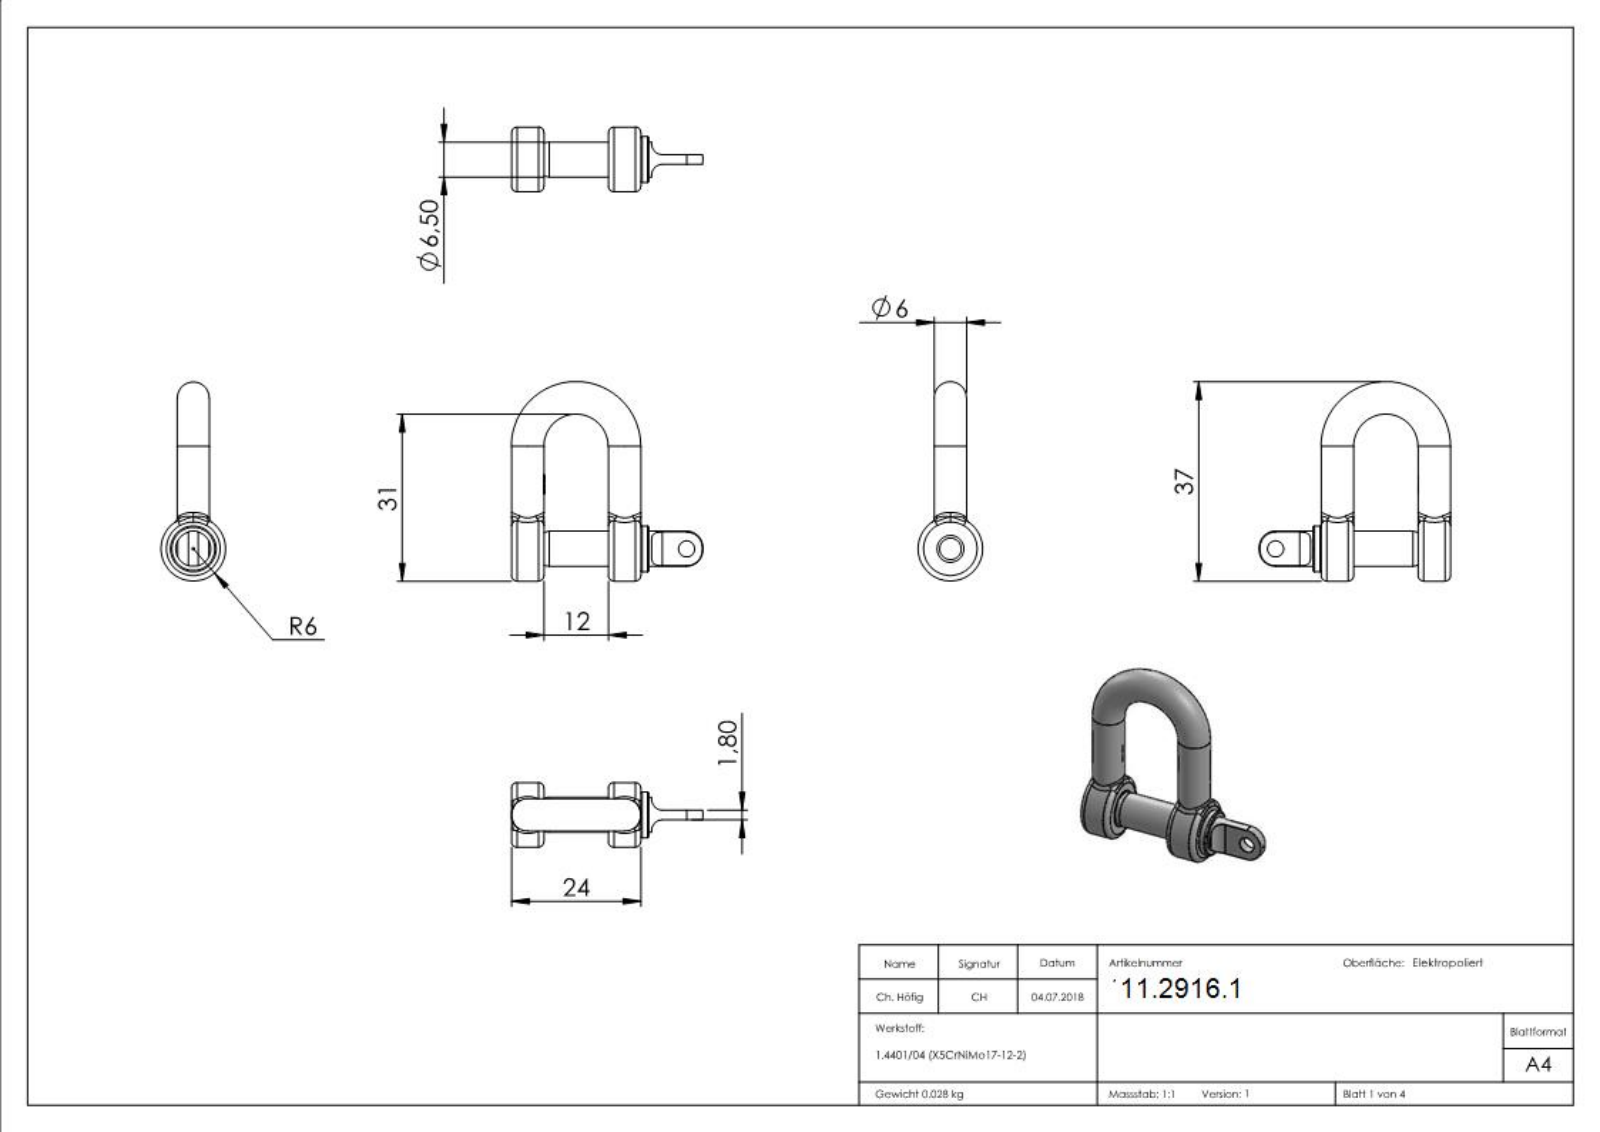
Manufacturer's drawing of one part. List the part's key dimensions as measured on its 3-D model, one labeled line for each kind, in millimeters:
Part name (STEP PRODUCT): 1000500X Teil1_10005006 Teil1; 10005006; 1000500X Teil2_10005006 Teil2
STEP written by: SolidWorks 2015 (CONFIG_CONTROL_DESIGN)
Units: millimetres
Bodies: 2 solids, 305 faces (74 planar, 64 cylindrical, 167 other)
Overall size (bounding box): 37 × 35.51 × 12
Volume: 3 508 mm³ · Surface area: 2 679 mm²
Round holes (diameter × count): ⌀3 ×1, ⌀5 ×1
Round bosses / shafts (diameter × count): ⌀6 ×3, ⌀12 ×1, ⌀8.5 ×1, ⌀6.5 ×1
Partial cylindrical surfaces — rounded edges, fillets, slot ends (radius × count): R2 ×2, R2.98 ×1
Main face-to-face distances: 6, 18, 24, 12, 1.8, 25.5, 19.5, 7.5, 1.5, 0.5
